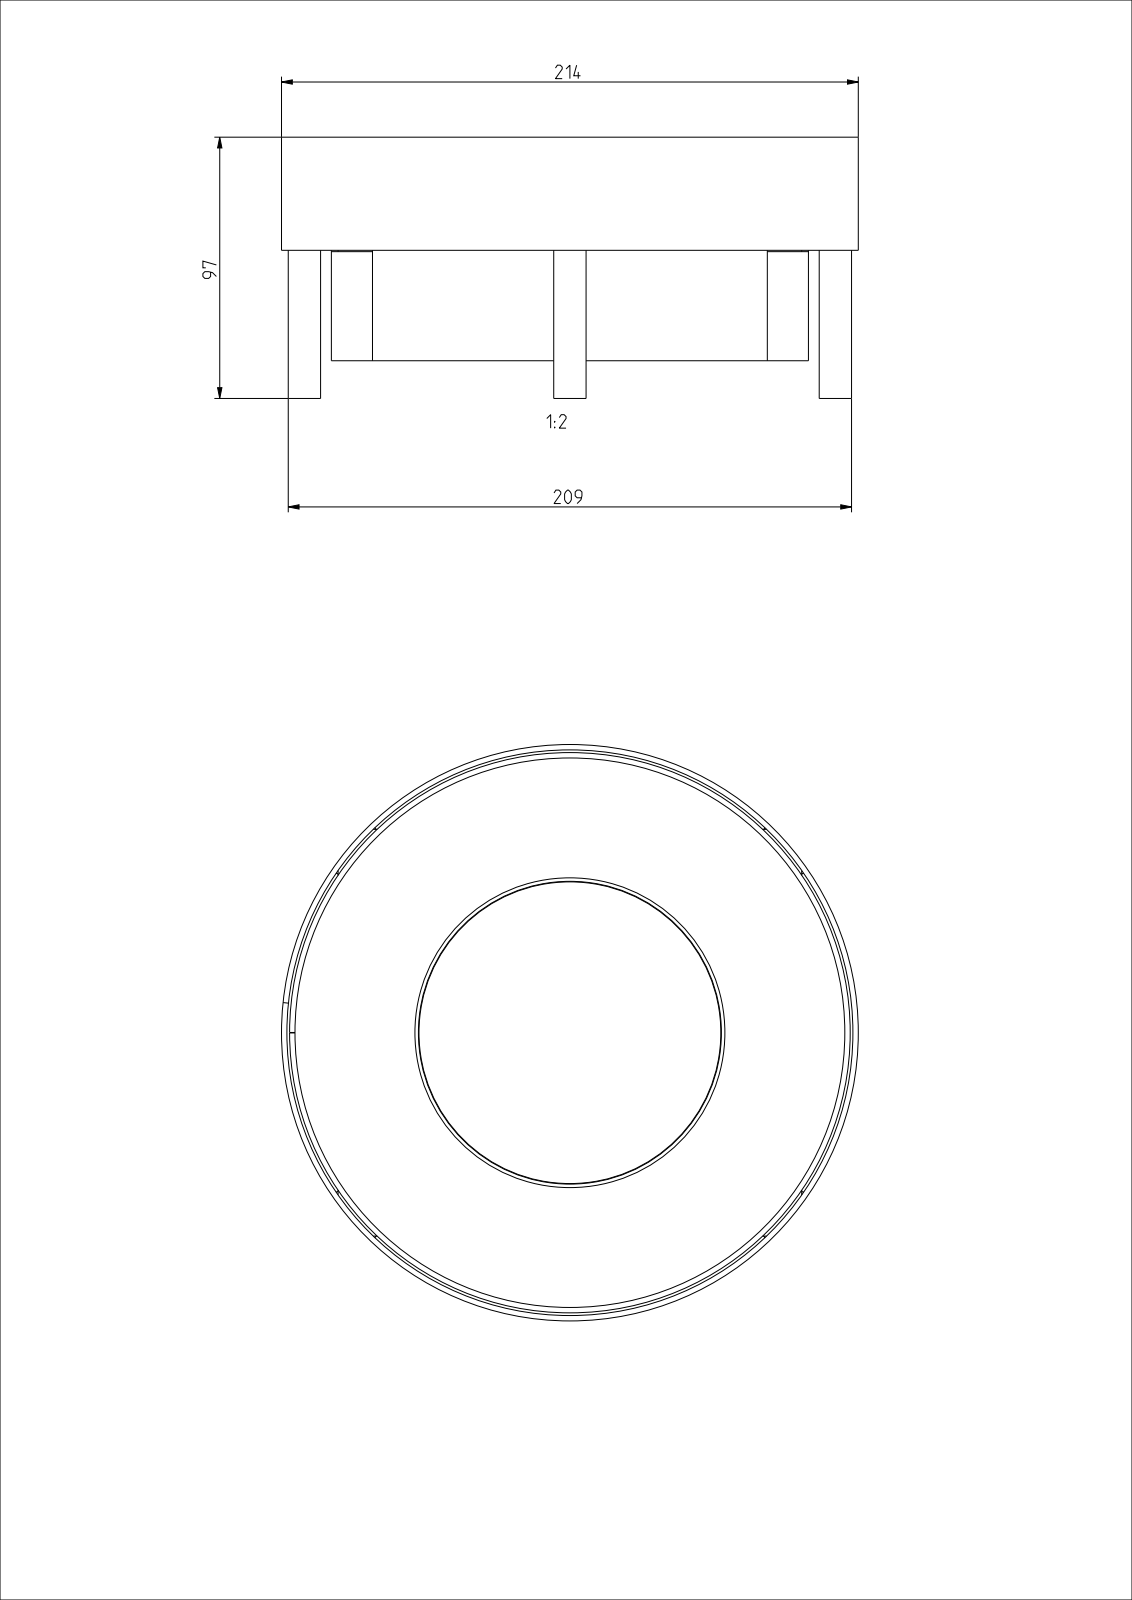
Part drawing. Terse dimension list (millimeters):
name: T-00671; T-00672; T-00673; T-00677 (+8 more)
written by: CREO PARAMETRIC BY PTC INC, 2022024 (AUTOMOTIVE_DESIGN)
unit: mm
bodies: 17 solids, 254 faces (115 planar, 129 cylindrical, 10 other)
size: 214 × 214 × 97
volume: 544 916 mm³; area: 363 070 mm²
holes: 6× ⌀3.8, 4× ⌀5, 4× ⌀6.8, 4× ⌀8.5, 4× ⌀10.1, 3× ⌀4.5, 1× ⌀80.59, 1× ⌀90, 1× ⌀101, 1× ⌀107, 1× ⌀108.6, 1× ⌀111.4
bosses: 4× ⌀12, 4× ⌀9.85, 1× ⌀214, 1× ⌀208, 1× ⌀207, 1× ⌀204, 1× ⌀115, 1× ⌀111.6
rounds: 8× R0.5, 3× R5, 1× R43
face distances: 2, 12, 10, 15, 2.5, 25, 27, 37, 153.5, 17
hole spacings: 69.91, 150.39, 41.16, 44.08, 63.64, 90, 95.62, 97.39
